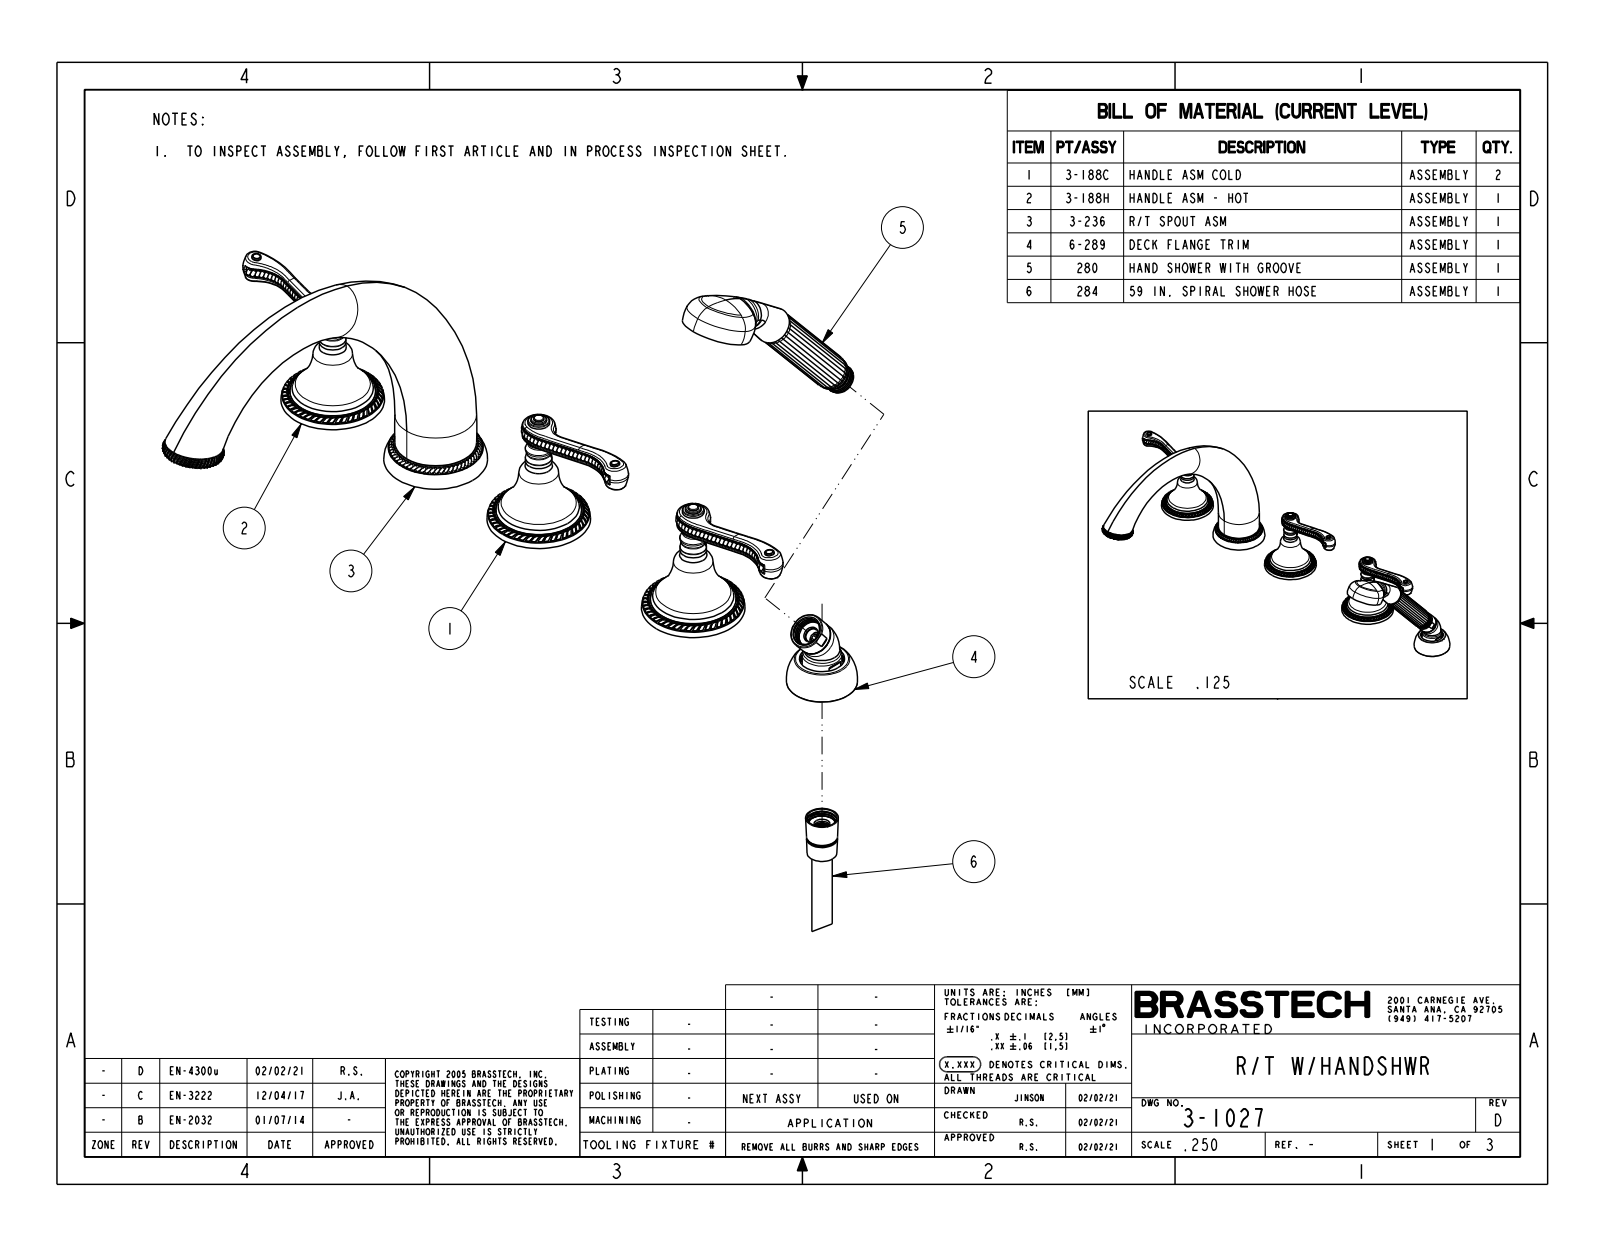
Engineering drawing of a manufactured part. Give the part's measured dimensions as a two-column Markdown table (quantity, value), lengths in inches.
| quantity | value |
| --- | --- |
| part name | 3-1027 |
| STEP written by | CREO PARAMETRIC BY PTC INC, 2018400 (CONFIG_CONTROL_DESIGN) |
| units | inches |
| bodies | 5 solids, 2990 faces (426 planar, 569 cylindrical, 1995 other) |
| overall size | 23.342 × 11.682 × 7.801 |
| volume | 63.29 in³ |
| surface area | 221.1 in² |
| round holes (diameter × count) | 0.046 × 52 |
| round bosses / shafts (diameter × count) | 0.26 × 6, 0.73 × 4, 2.35 × 3, 0.7 × 3, 0.6 × 3, 0.44 × 3, 0.4 × 3, 0.29 × 3 |
| partial cylindrical surfaces (radius × count) | 0.15 × 147, 0.09 × 75, 0.12 × 72, 0.224 × 50, 0.05 × 6, 11 × 6, 0.121 × 3, 0.137 × 3 |
| main face-to-face distances | 3.23, 0.49, 2.74, 0.29, 2.45, 2.94, 1.94, 1.65, 0.8, 1.29 |
| hole center spacings | 0.497, 0.367, 0.184, 0.185, 0.187, 0.355, 0.185, 0.535 |
